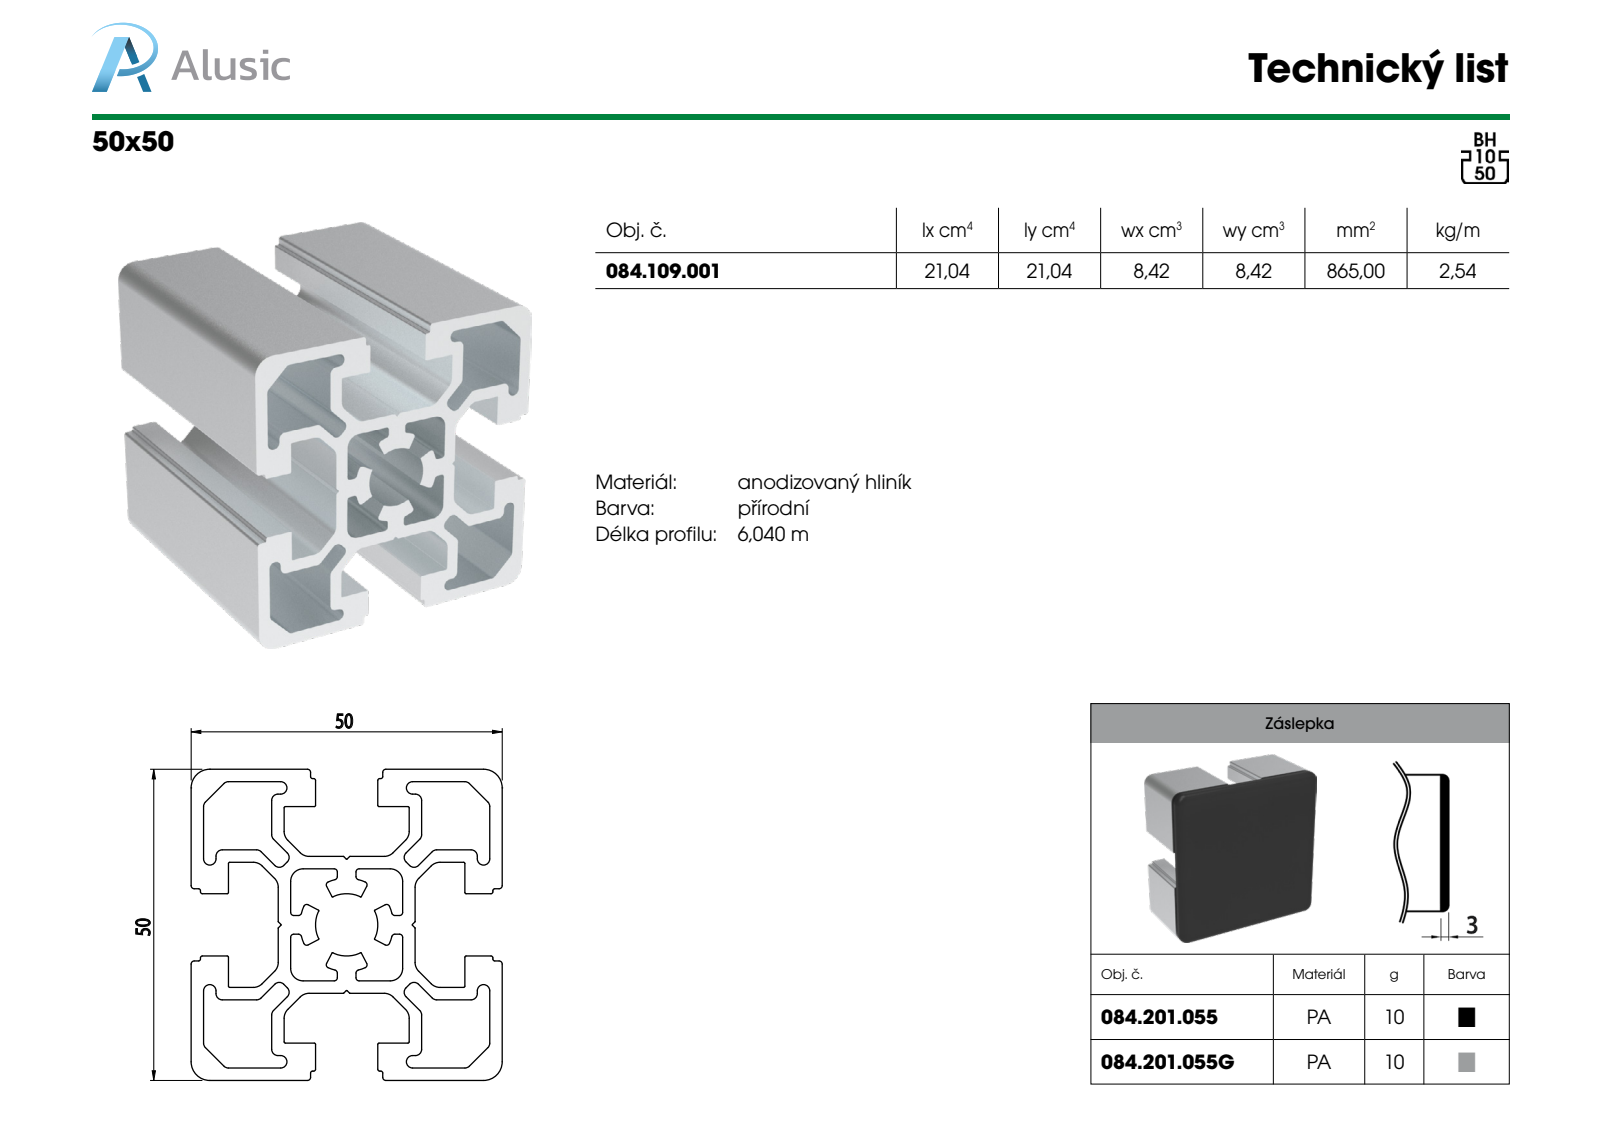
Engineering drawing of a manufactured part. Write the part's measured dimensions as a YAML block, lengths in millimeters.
part_name: "084.109.001"
step_written_by: "SolidWorks 2018 (AUTOMOTIVE_DESIGN)"
units: millimeters
bodies: {solids: 1, faces: 308, planar: 138, cylindrical: 170, other: 0}
overall_size: [100, 50, 50]
volume: 86449
surface_area: 72915
partial_cylinders:
  - {radius: 1, count: 40}
  - {radius: 0.5, count: 32}
  - {radius: 0.1, count: 20}
  - {radius: 2, count: 20}
  - {radius: 0.2, count: 16}
  - {radius: 0.3, count: 16}
  - {radius: 3, count: 4}
  - {radius: 5, count: 1}
face_to_face_distances: [14, 2, 34, 12.95, 35.05, 1.05, 20, 16, 21.05, 6]
